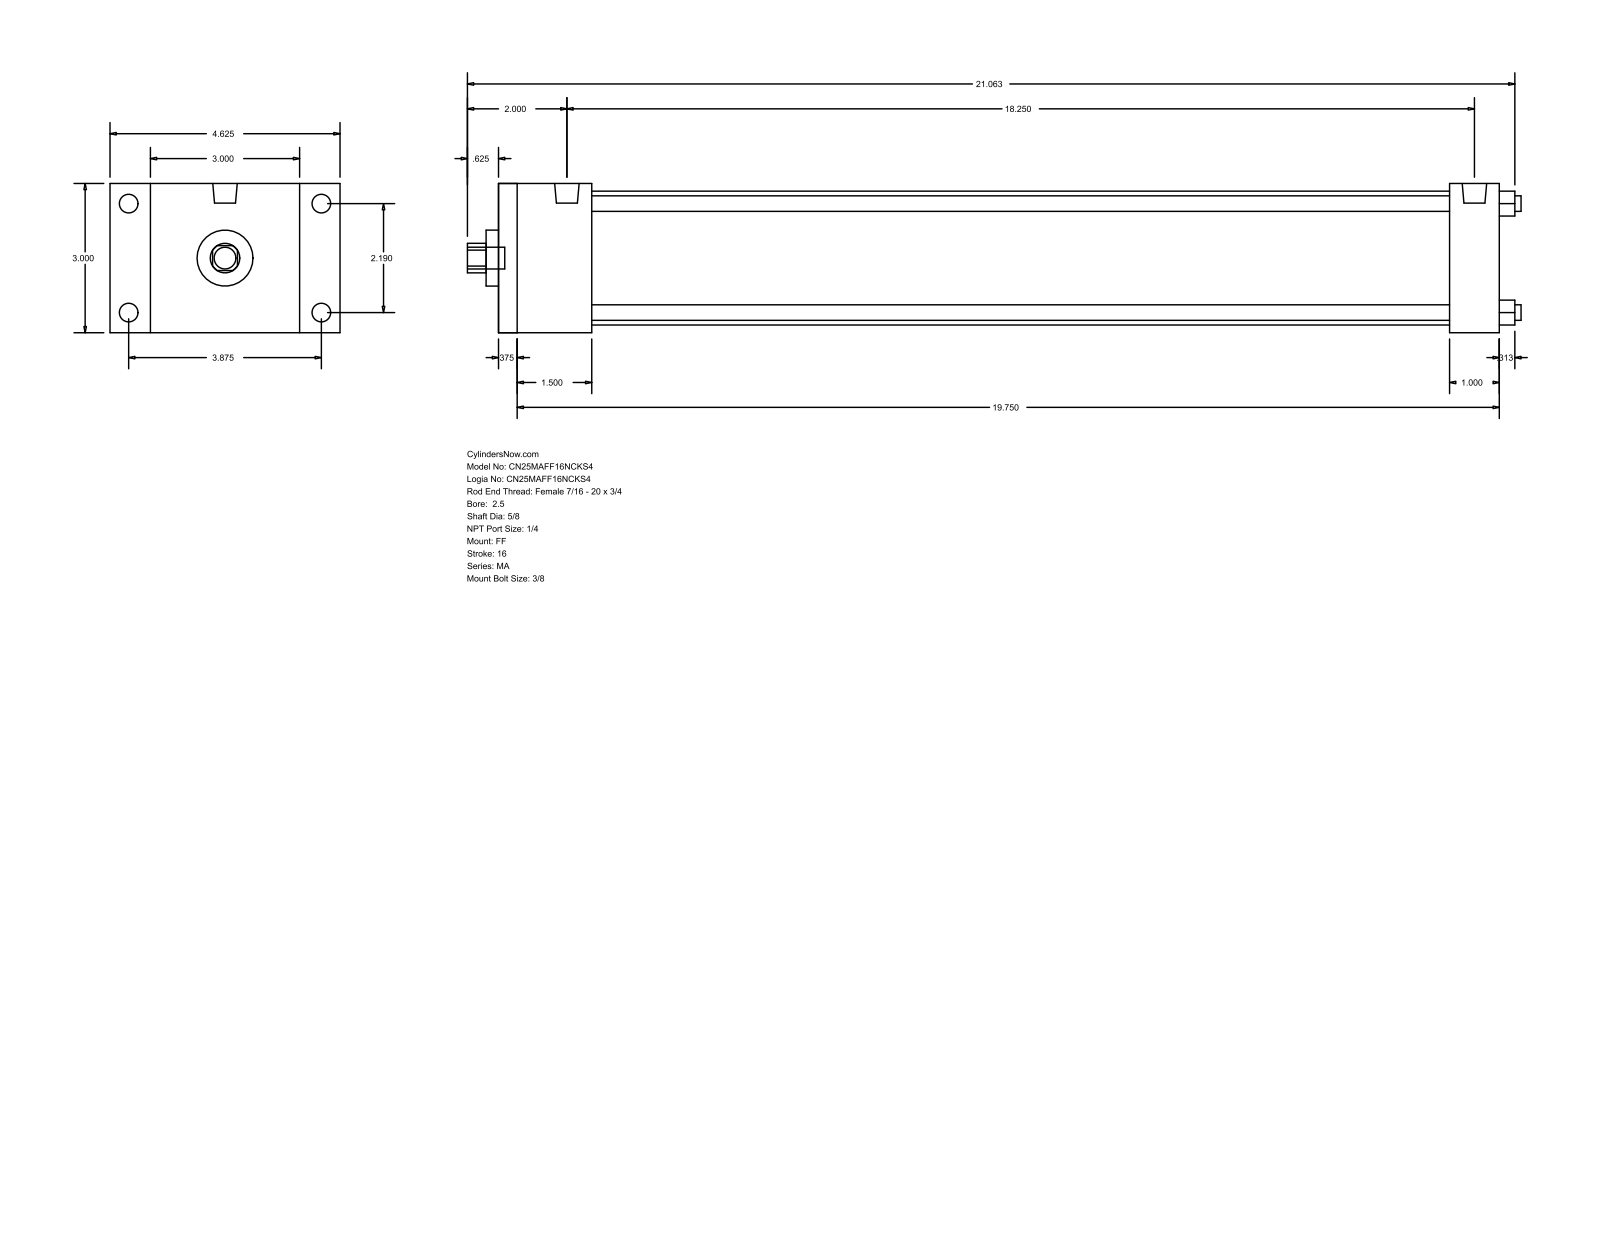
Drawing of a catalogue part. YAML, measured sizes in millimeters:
part_name: "MA_FF__0250_0.625"
step_written_by: "GSSL Pune (CONFIG_CONTROL_DESIGN)"
units: millimeters
bodies: {solids: 0, faces: 92, planar: 64, cylindrical: 28, other: 0}
overall_size: [538.16, 117.47, 76.2]
round_holes:
  - {diameter: 7.94, count: 4}
  - {diameter: 15.88, count: 1}
  - {diameter: 28.57, count: 1}
  - {diameter: 68.33, count: 1}
round_bosses_or_shafts:
  - {diameter: 9.53, count: 4}
  - {diameter: 7.94, count: 4}
  - {diameter: 12.49, count: 2}
  - {diameter: 11.11, count: 1}
partial_cylinders:
  - {radius: 7.54, count: 1}
face_to_face_distances: [76.2, 511.17, 9.52, 501.65, 25.4, 47.62, 485.77, 38.1, 476.25, 438.15]
hole_center_spacings: [39.33, 55.62, 78.66]
